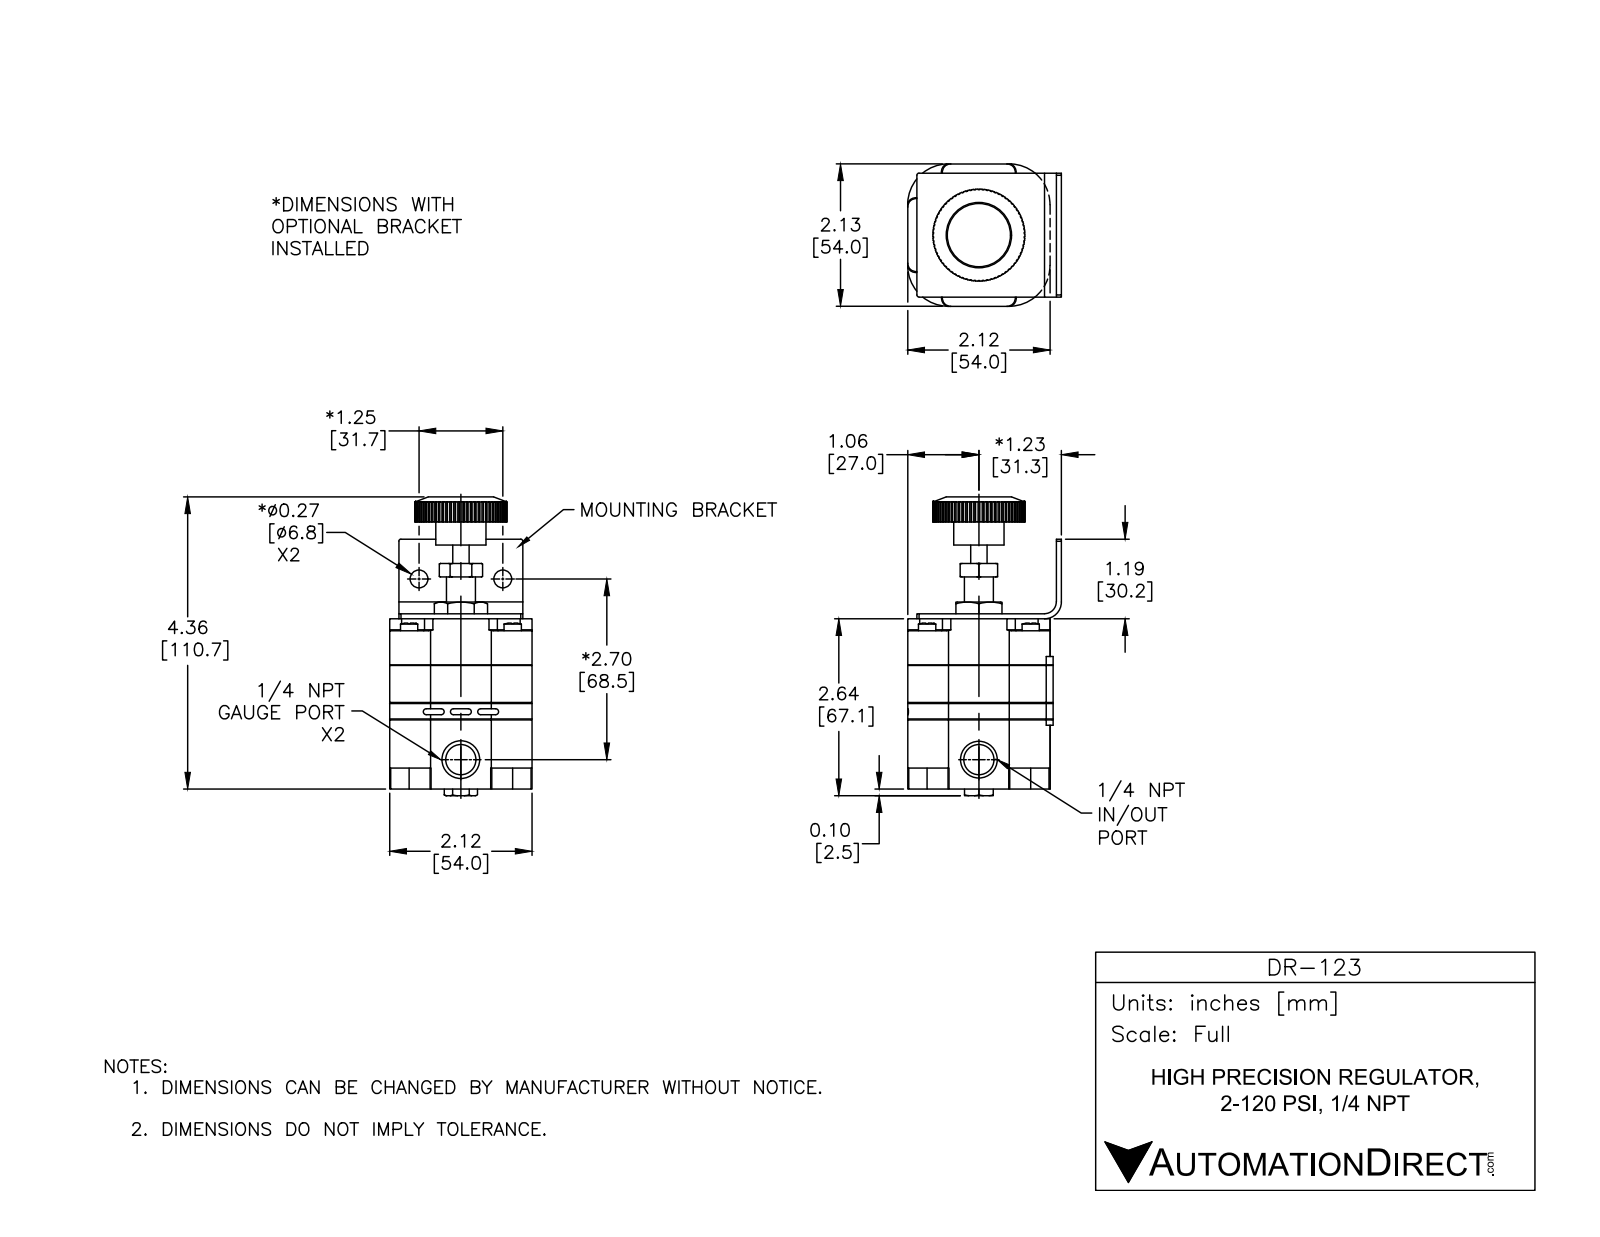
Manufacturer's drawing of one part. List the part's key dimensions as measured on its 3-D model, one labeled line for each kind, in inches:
Part name (STEP PRODUCT): DR-123
STEP written by: SolidWorks 2015 (CONFIG_CONTROL_DESIGN)
Units: inches
Bodies: 15 solids, 763 faces (474 planar, 203 cylindrical, 86 other)
Overall size (bounding box): 4.46 × 2.171 × 2.125
Volume: 10.36 in³ · Surface area: 70.85 in²
Round holes (diameter × count): ⌀0.438 ×2, ⌀0.097 ×1, ⌀0.215 ×1, ⌀0.335 ×1, ⌀0.43 ×1, ⌀0.44 ×1, ⌀0.943 ×1
Round bosses / shafts (diameter × count): ⌀0.258 ×4, ⌀0.75 ×1, ⌀0.745 ×1, ⌀0.432 ×1, ⌀0.414 ×1, ⌀0.245 ×1
Partial cylindrical surfaces — rounded edges, fillets, slot ends (radius × count): R0.015 ×20, R0.055 ×16, R0.125 ×8, R0.045 ×6, R0.266 ×4, R0.313 ×4, R0.609 ×4, R0.203 ×1
Main face-to-face distances: 0.563, 0.26, 0.823, 0.259, 0.822, 0.563, 0.563, 2.125, 1.031, 1.291
Hole centre spacings: 0.5, 1.153, 1.163
